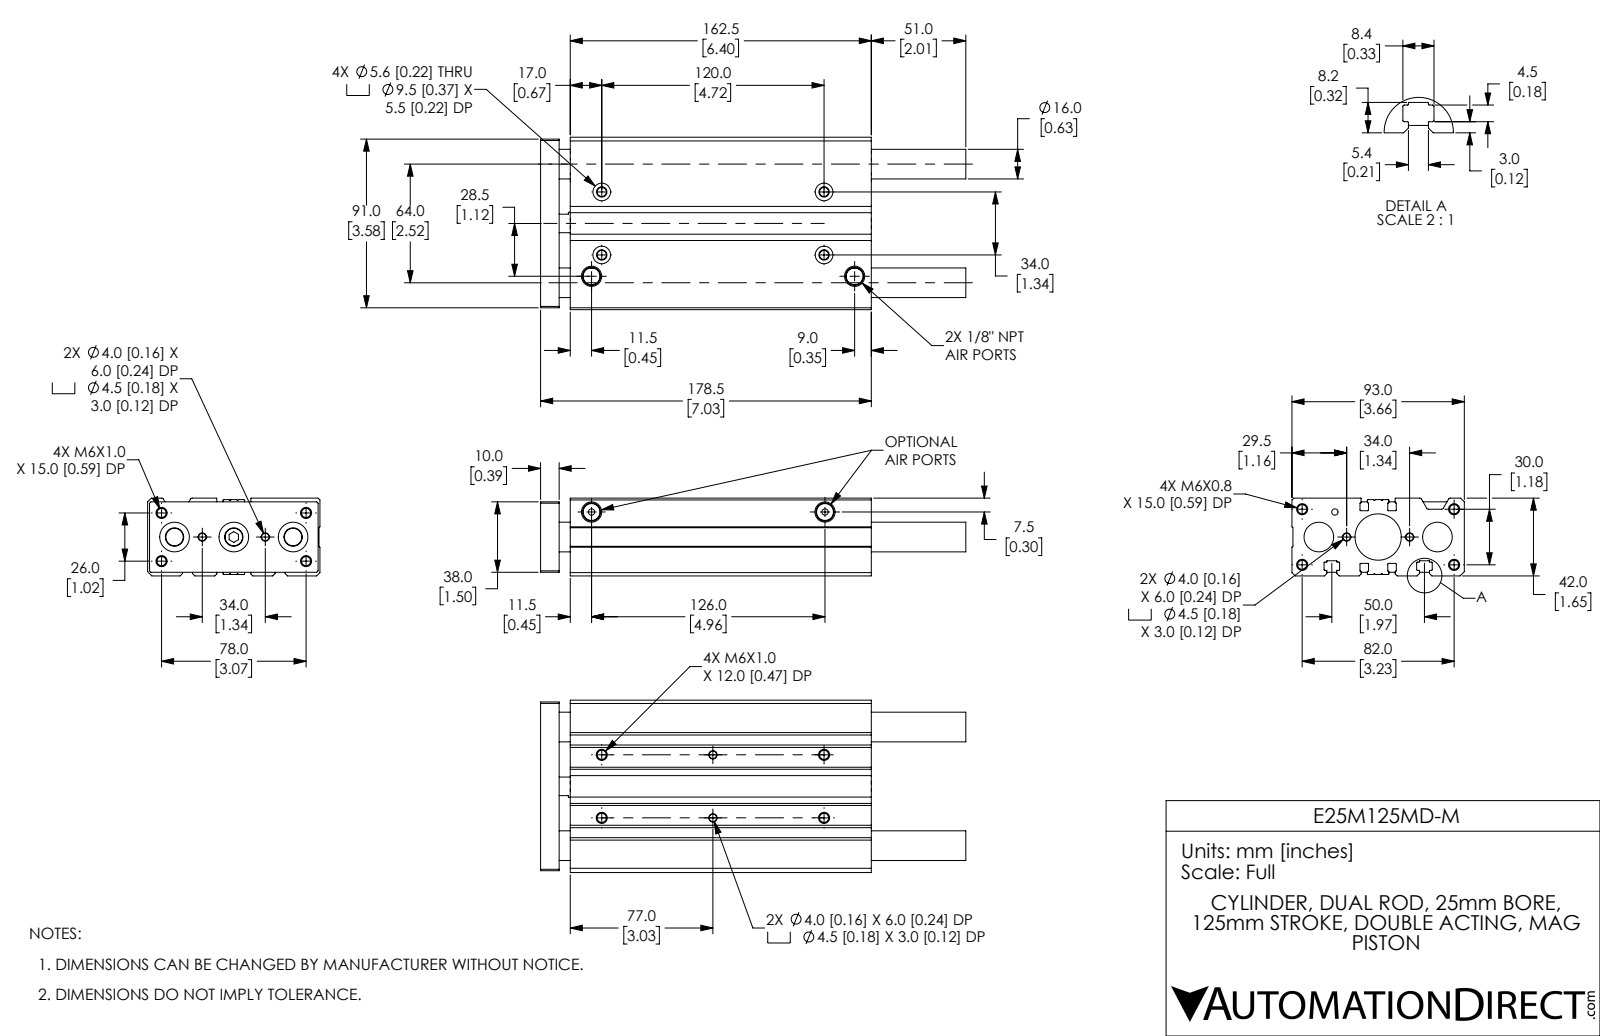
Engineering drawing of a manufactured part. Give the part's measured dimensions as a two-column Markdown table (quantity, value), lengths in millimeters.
| quantity | value |
| --- | --- |
| part name | E25M125MD-M_BODY; E25M125MD-M_ENDPLATE; E25M125MD-M |
| STEP written by | SolidWorks 2019 (CONFIG_CONTROL_DESIGN) |
| units | millimeters |
| bodies | 5 solids, 423 faces (139 planar, 190 cylindrical, 94 other) |
| overall size | 229.5 × 93 × 42 |
| volume | 578 379 mm³ |
| surface area | 144 363 mm² |
| round holes (diameter × count) | 4.92 × 10, 4 × 4, 4.5 × 4, 5.6 × 4, 9.5 × 4, 8 × 3, 16 × 3, 3.43 × 2, 4.92 × 2, 9.91 × 2, 3.43 × 1, 16 × 1 |
| round bosses / shafts (diameter × count) | 12 × 1, 9.91 × 1 |
| partial cylindrical surfaces (radius × count) | 0.2 × 32, 0.4 × 28, 1 × 4, 0.3 × 2 |
| main face-to-face distances | 42, 6, 93, 0.8, 34.4, 15, 35.2, 16, 10, 41.2 |
| hole center spacings | 2.83, 14.76, 17.49, 25.55, 28.07, 28.3, 34, 41.11 |
